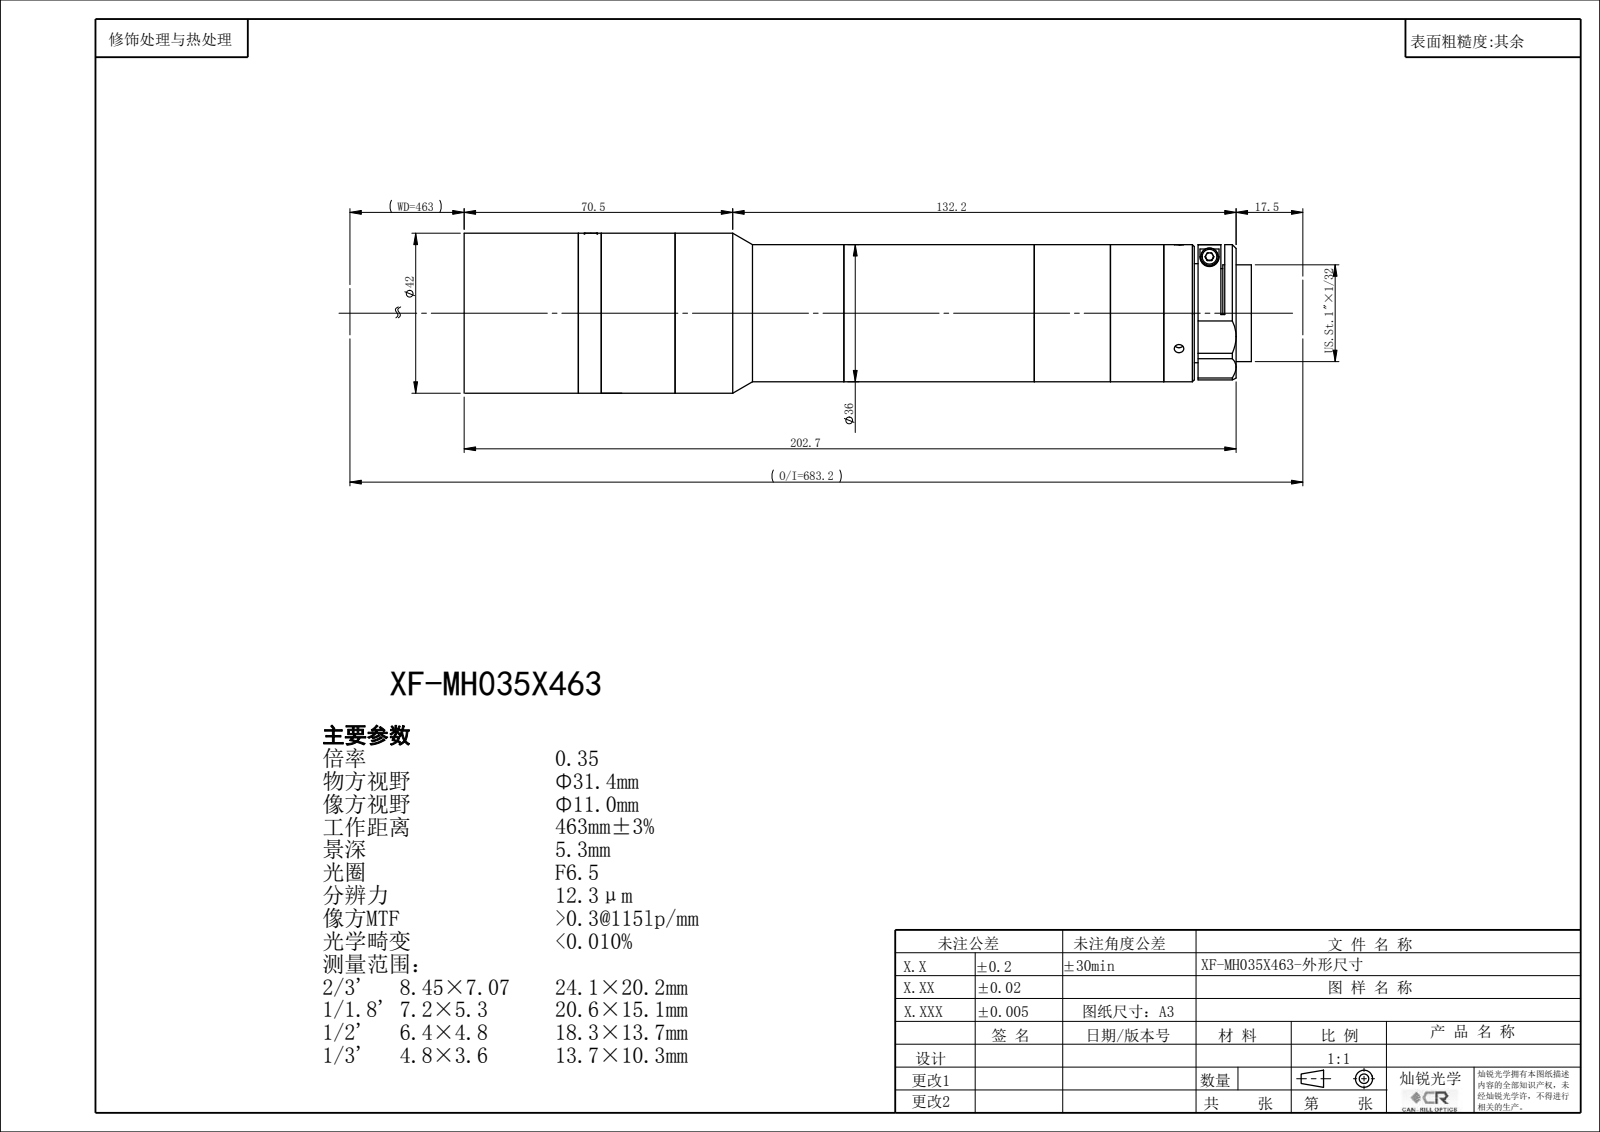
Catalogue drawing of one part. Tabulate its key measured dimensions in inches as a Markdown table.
| quantity | value |
| --- | --- |
| part name | XF-MH035X463 |
| STEP written by | SolidWorks 2022 (CONFIG_CONTROL_DESIGN) |
| units | inches |
| bodies | 0 solids, 140 faces (74 planar, 44 cylindrical, 22 other) |
| overall size | 8.136 × 1.654 × 1.654 |
| round holes (diameter × count) | 0.098 × 3, 0.882 × 1, 0.945 × 1, 1.039 × 1, 1.299 × 1, 1.433 × 1 |
| round bosses / shafts (diameter × count) | 1.654 × 1, 1.417 × 1, 1.339 × 1, 1 × 1 |
| main face-to-face distances | 0.746, 0.787, 0.059, 0.687, 7.233, 7.92, 7.979, 0.236, 6.682, 0.551 |
